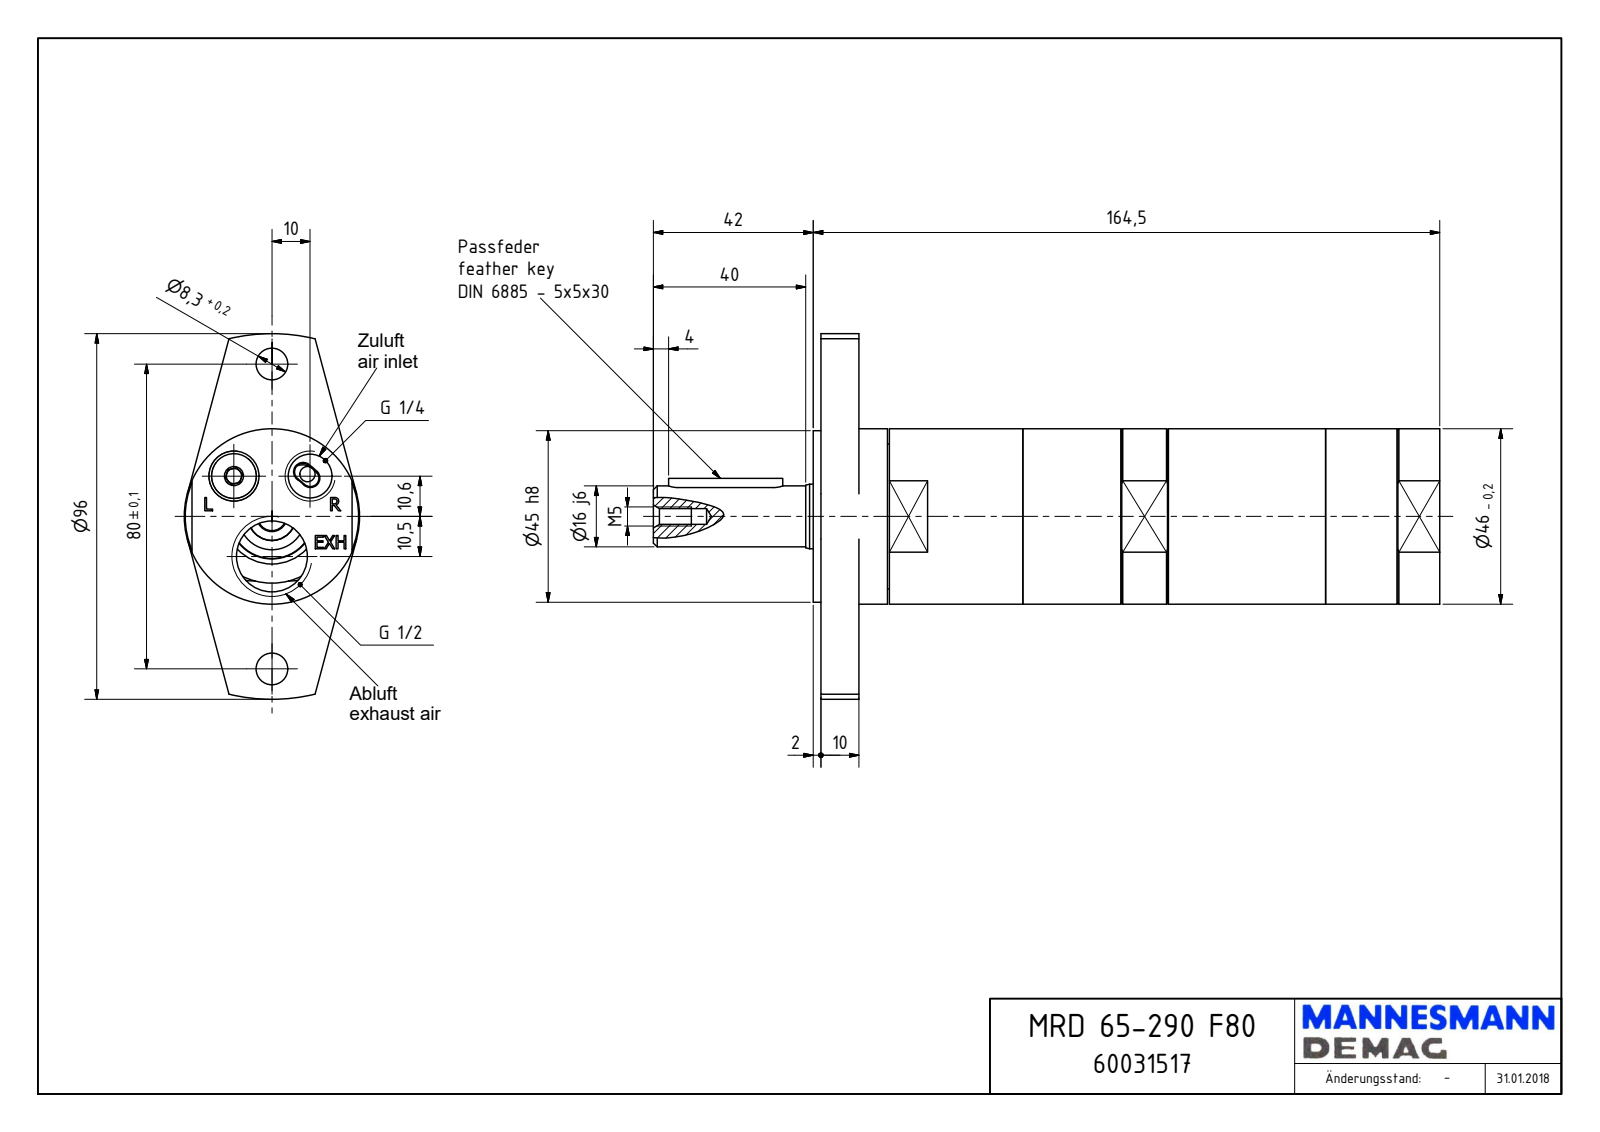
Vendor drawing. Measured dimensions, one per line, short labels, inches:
name: MRD 65-290 F80_60031517
written by: Autodesk Inventor 2018 (AUTOMOTIVE_DESIGN)
unit: in
bodies: 1 solid, 173 faces (113 planar, 33 cylindrical, 27 other)
size: 8.13 × 3.78 × 1.811
volume: 17.79 in³; area: 57.82 in²
holes: 2× ⌀0.327, 1× ⌀0.157, 1× ⌀0.163, 1× ⌀0.451, 1× ⌀0.689, 1× ⌀0.733, 1× ⌀1.496, 1× ⌀1.511
bosses: 1× ⌀1.811, 1× ⌀1.772, 1× ⌀1.315, 1× ⌀0.667, 1× ⌀0.63
rounds: 2× R0.098, 2× R0.197, 1× R0.225, 1× R1.89
face distances: 0.394, 0.079, 0.472, 6.004, 6.476, 6.398, 1.654, 0.315, 5.689, 0.709
hole spacings: 0.574, 0.919, 1.222, 1.575, 2.031, 0.413, 0.787, 1.161
